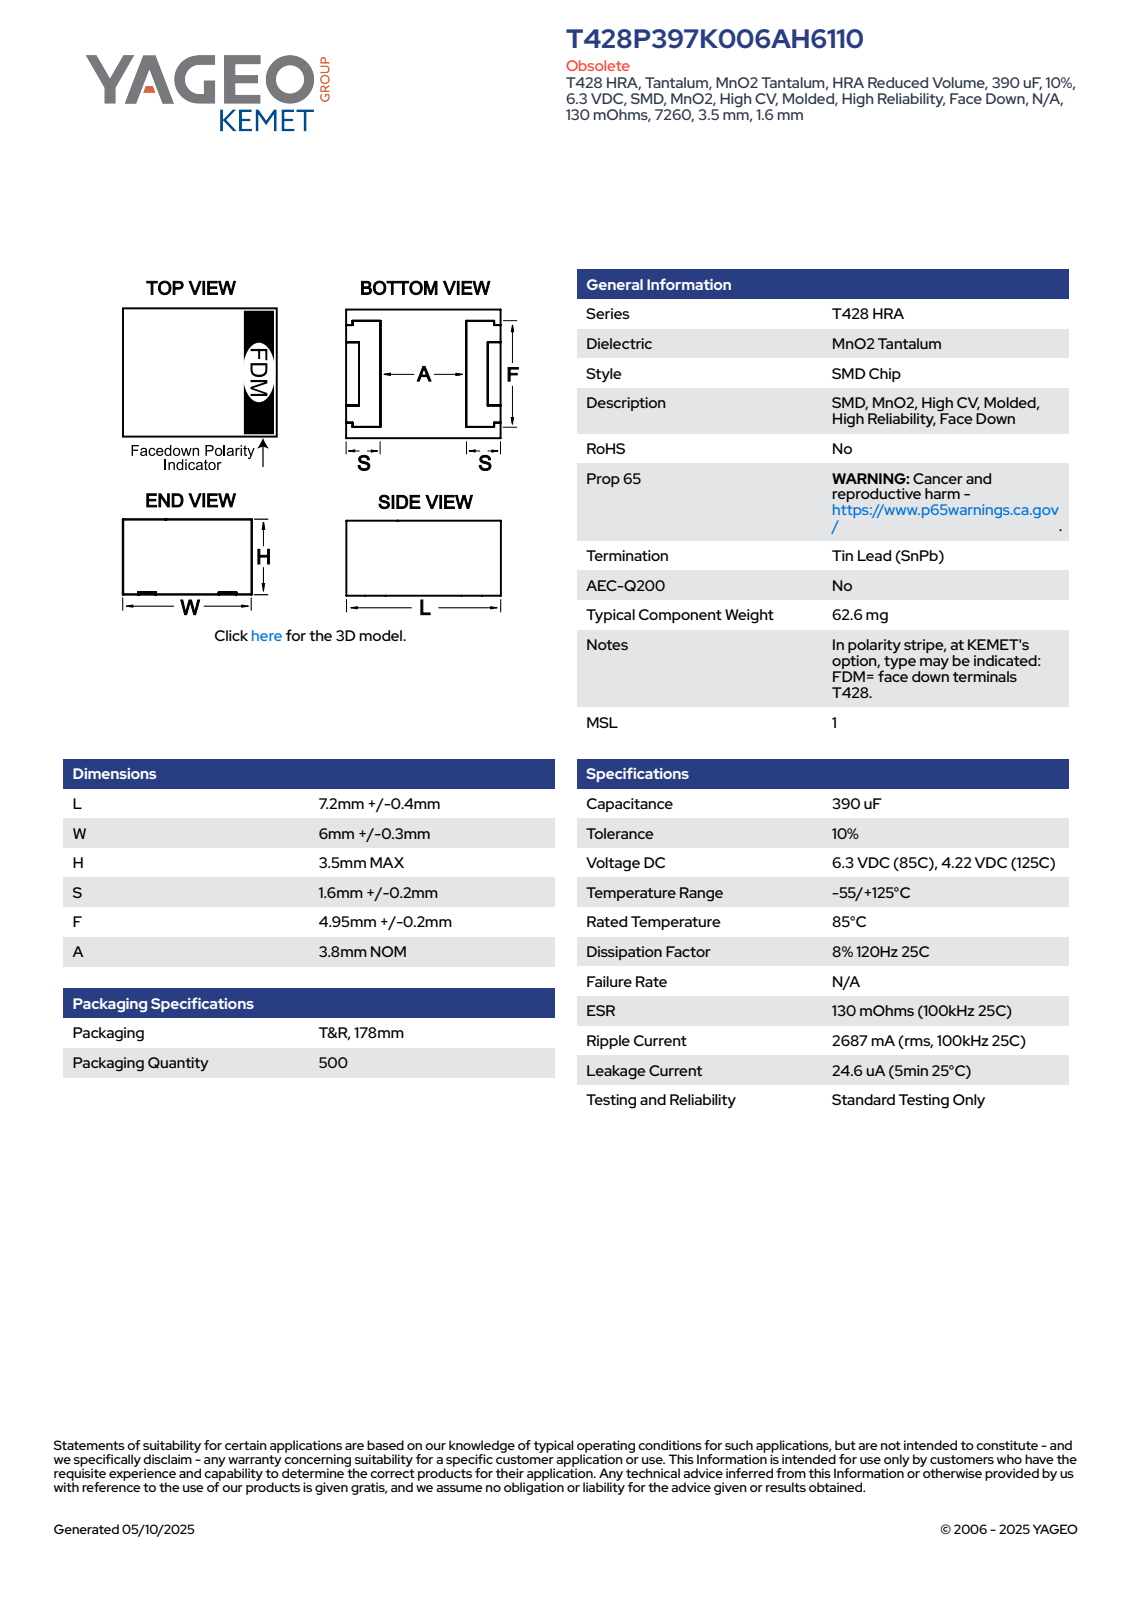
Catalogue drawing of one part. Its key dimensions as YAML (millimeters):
part_name: "CTSM_7260_L7.60W6.3H3.50S1.6F4.95; CTSM_Case_Cathode_10; CTSM_Case_Anode_10; CTSM_Case_Top_10 (+1 more)"
step_written_by: "SolidWorks 2014 (AUTOMOTIVE_DESIGN)"
units: millimeters
bodies: {solids: 7, faces: 89, planar: 85, cylindrical: 4, other: 0}
overall_size: [7.6, 6.3, 3.5]
volume: 153
surface_area: 337
face_to_face_distances: [1.6, 3.37, 1.77, 6.27, 7.31, 7.47, 1.73, 3.5, 7.34, 7.6]
